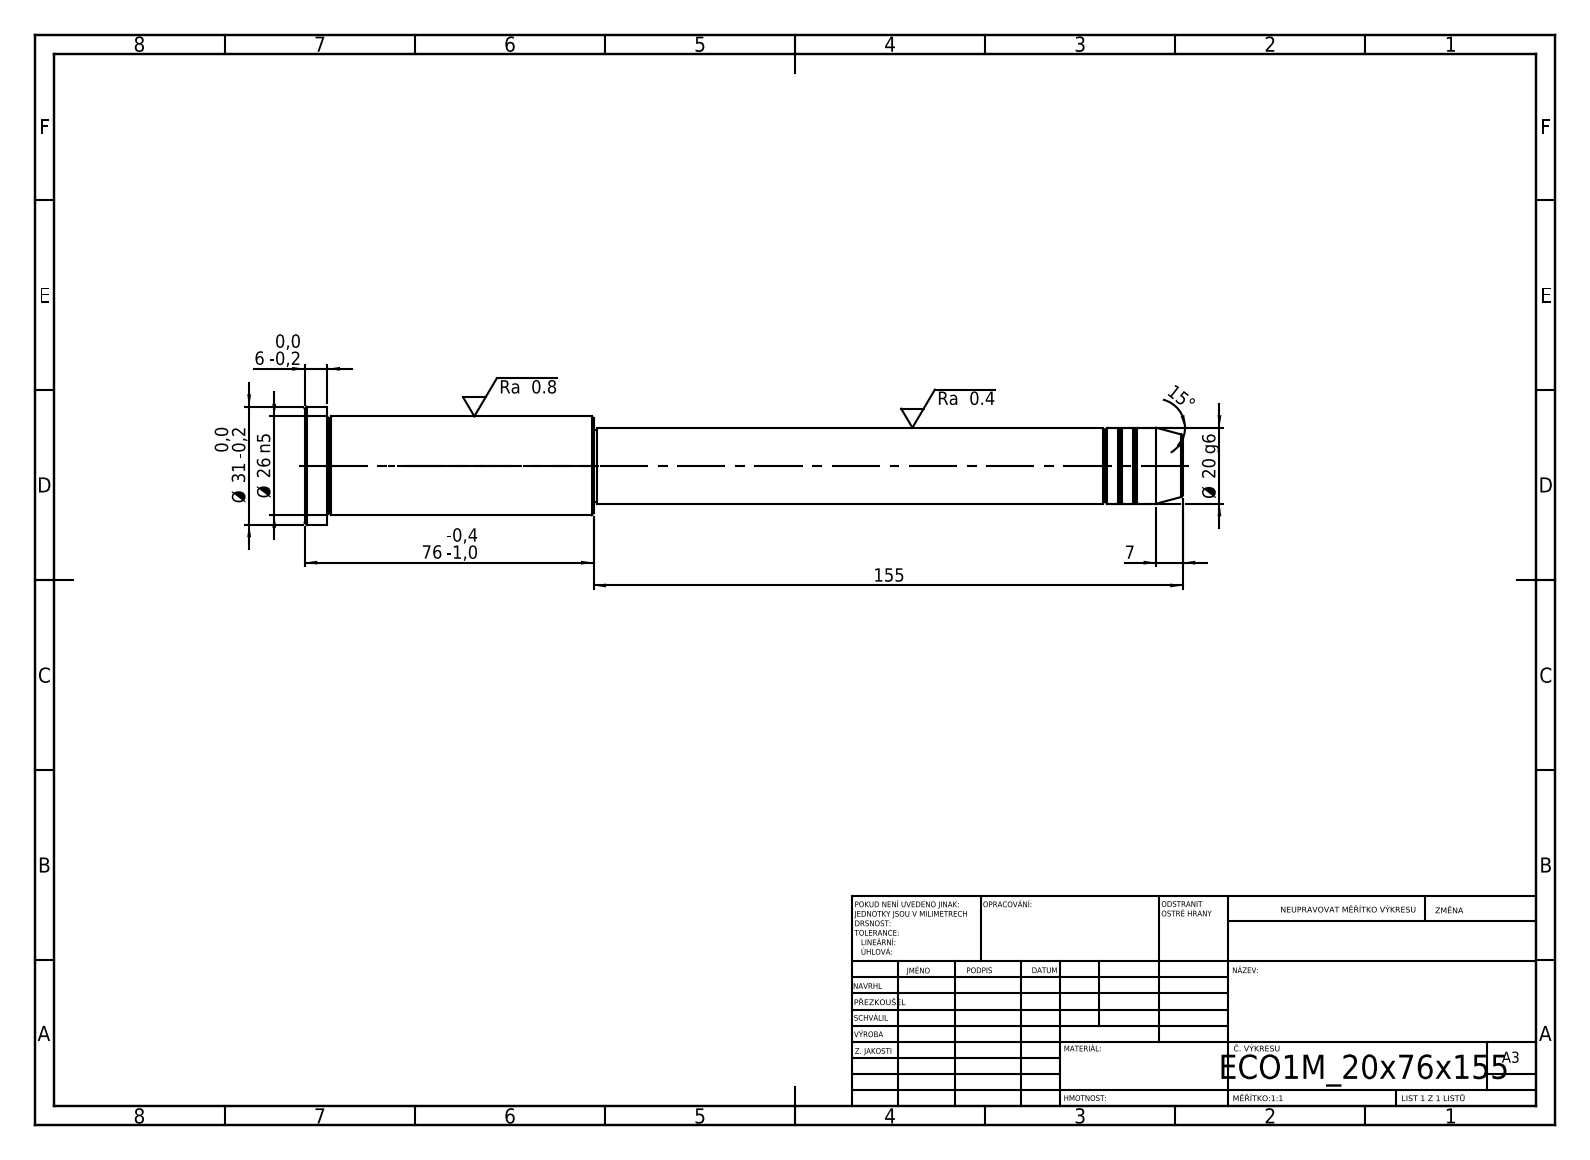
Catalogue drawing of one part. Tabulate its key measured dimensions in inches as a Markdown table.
| quantity | value |
| --- | --- |
| STEP written by | SolidWorks 2019 (CONFIG_CONTROL_DESIGN) |
| units | inches |
| bodies | 1 solid, 43 faces (5 planar, 14 cylindrical, 24 other) |
| overall size | 9.094 × 1.22 × 1.22 |
| volume | 5.483 in³ |
| surface area | 27.21 in² |
| round bosses / shafts (diameter × count) | 1.22 × 1, 1.024 × 1, 0.787 × 1, 0.748 × 1 |
| main face-to-face distances | 0.236, 2.756, 2.992, 6.102, 8.858, 9.094, 6.063, 0.039, 2.795, 3.031 |
